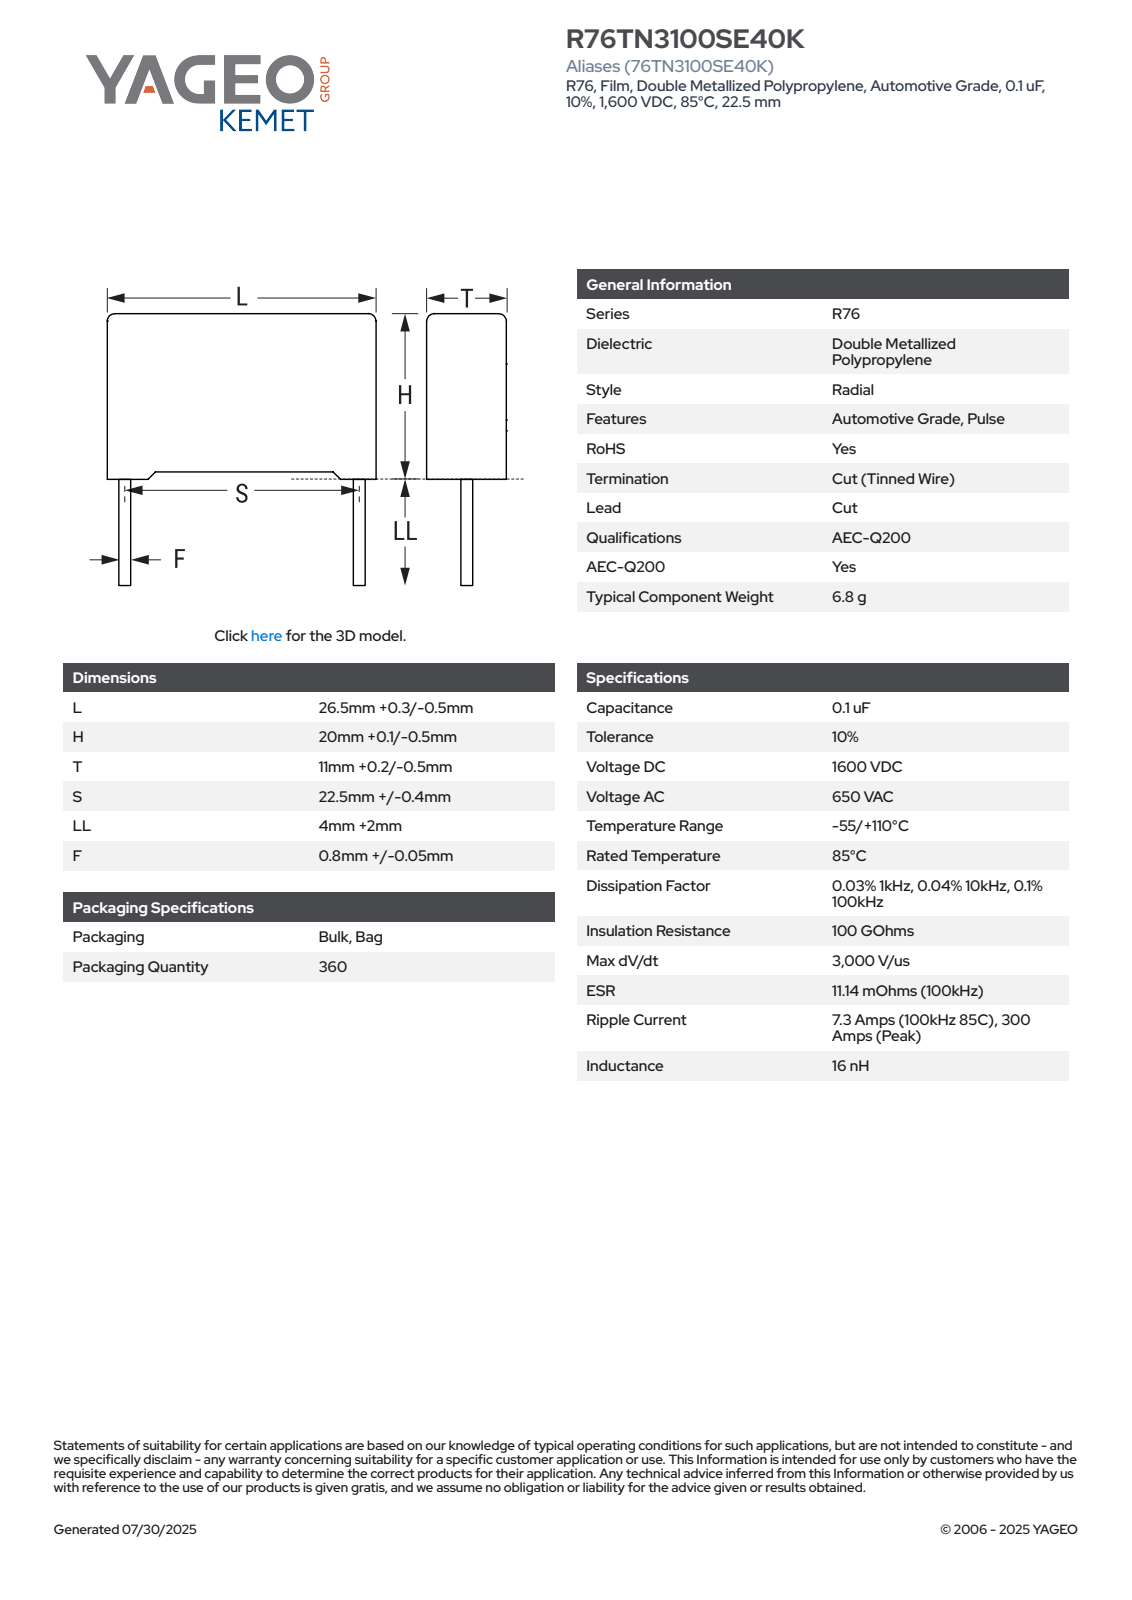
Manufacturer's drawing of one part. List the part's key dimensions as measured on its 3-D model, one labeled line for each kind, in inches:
Part name (STEP PRODUCT): CFR_RB2_26.5X20X11_L26.8H20.1T11.2S22.5LL6F0.85
STEP written by: SolidWorks 2021 (AUTOMOTIVE_DESIGN)
Units: inches
Bodies: 4 solids, 85 faces (77 planar, 8 cylindrical, 0 other)
Overall size (bounding box): 1.055 × 1.028 × 0.441
Volume: 0.356 in³ · Surface area: 3.413 in²
Round bosses / shafts (diameter × count): ⌀0.033 ×2
Partial cylindrical surfaces — rounded edges, fillets, slot ends (radius × count): R0.02 ×4
Main face-to-face distances: 0.441, 0.762, 1.055, 0.764, 0.03, 0.027, 0.791, 0.035, 1.02, 0.441
